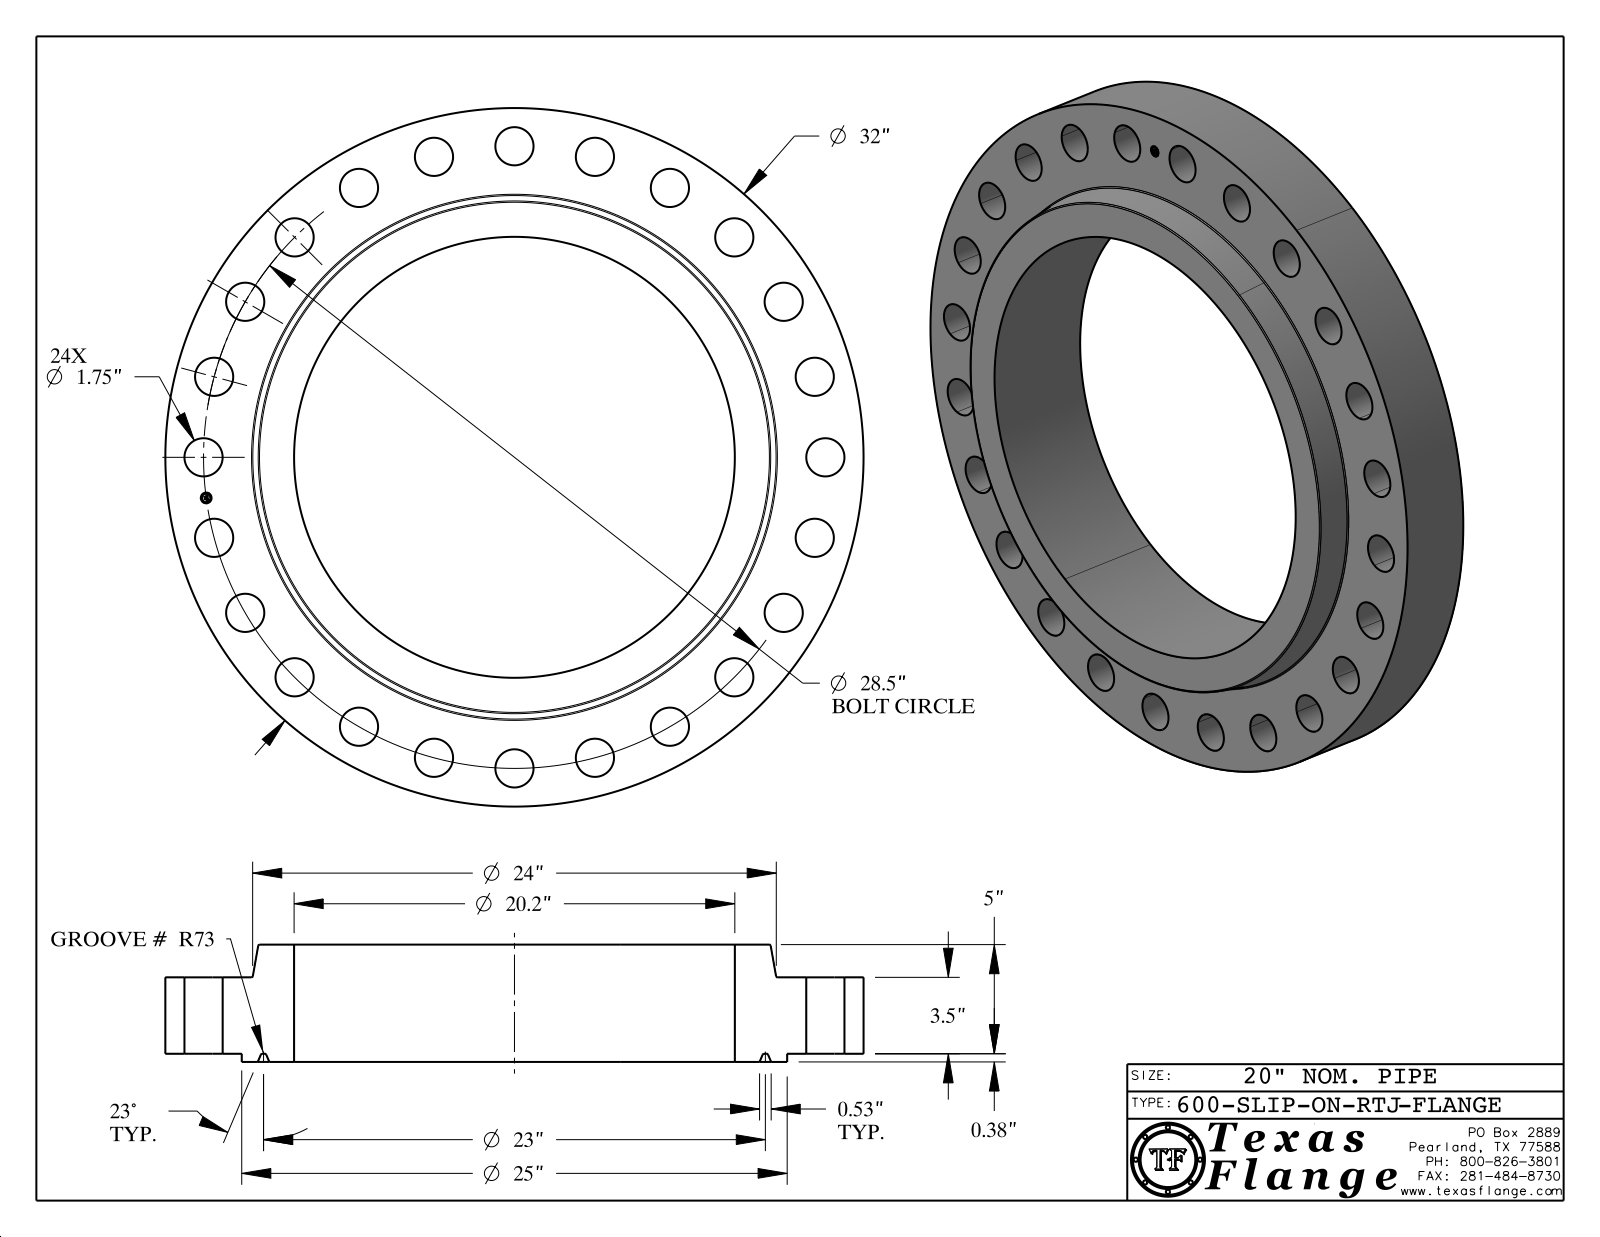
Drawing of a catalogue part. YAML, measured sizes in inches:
part_name: "600-SLIP-ON-RTJ"
step_written_by: "CATIA V5 STEP AP214 (AUTOMOTIVE_DESIGN)"
units: inches
bodies: {solids: 1, faces: 459, planar: 371, cylindrical: 74, other: 14}
overall_size: [32, 32, 5.375]
volume: 1728
surface_area: 2162
round_holes:
  - {diameter: 1.75, count: 24}
  - {diameter: 0.495, count: 1}
  - {diameter: 20.2, count: 1}
round_bosses_or_shafts:
  - {diameter: 0.03, count: 8}
  - {diameter: 32, count: 1}
  - {diameter: 25, count: 1}
  - {diameter: 0.39, count: 1}
face_to_face_distances: [3.5, 0.375, 3.875, 5.375, 5, 1.5, 0.015, 3.86, 3.485, 1.515]
hole_center_spacings: [14.25, 3.72, 7.376, 24.682, 26.331, 27.529, 20.153, 10.907]
